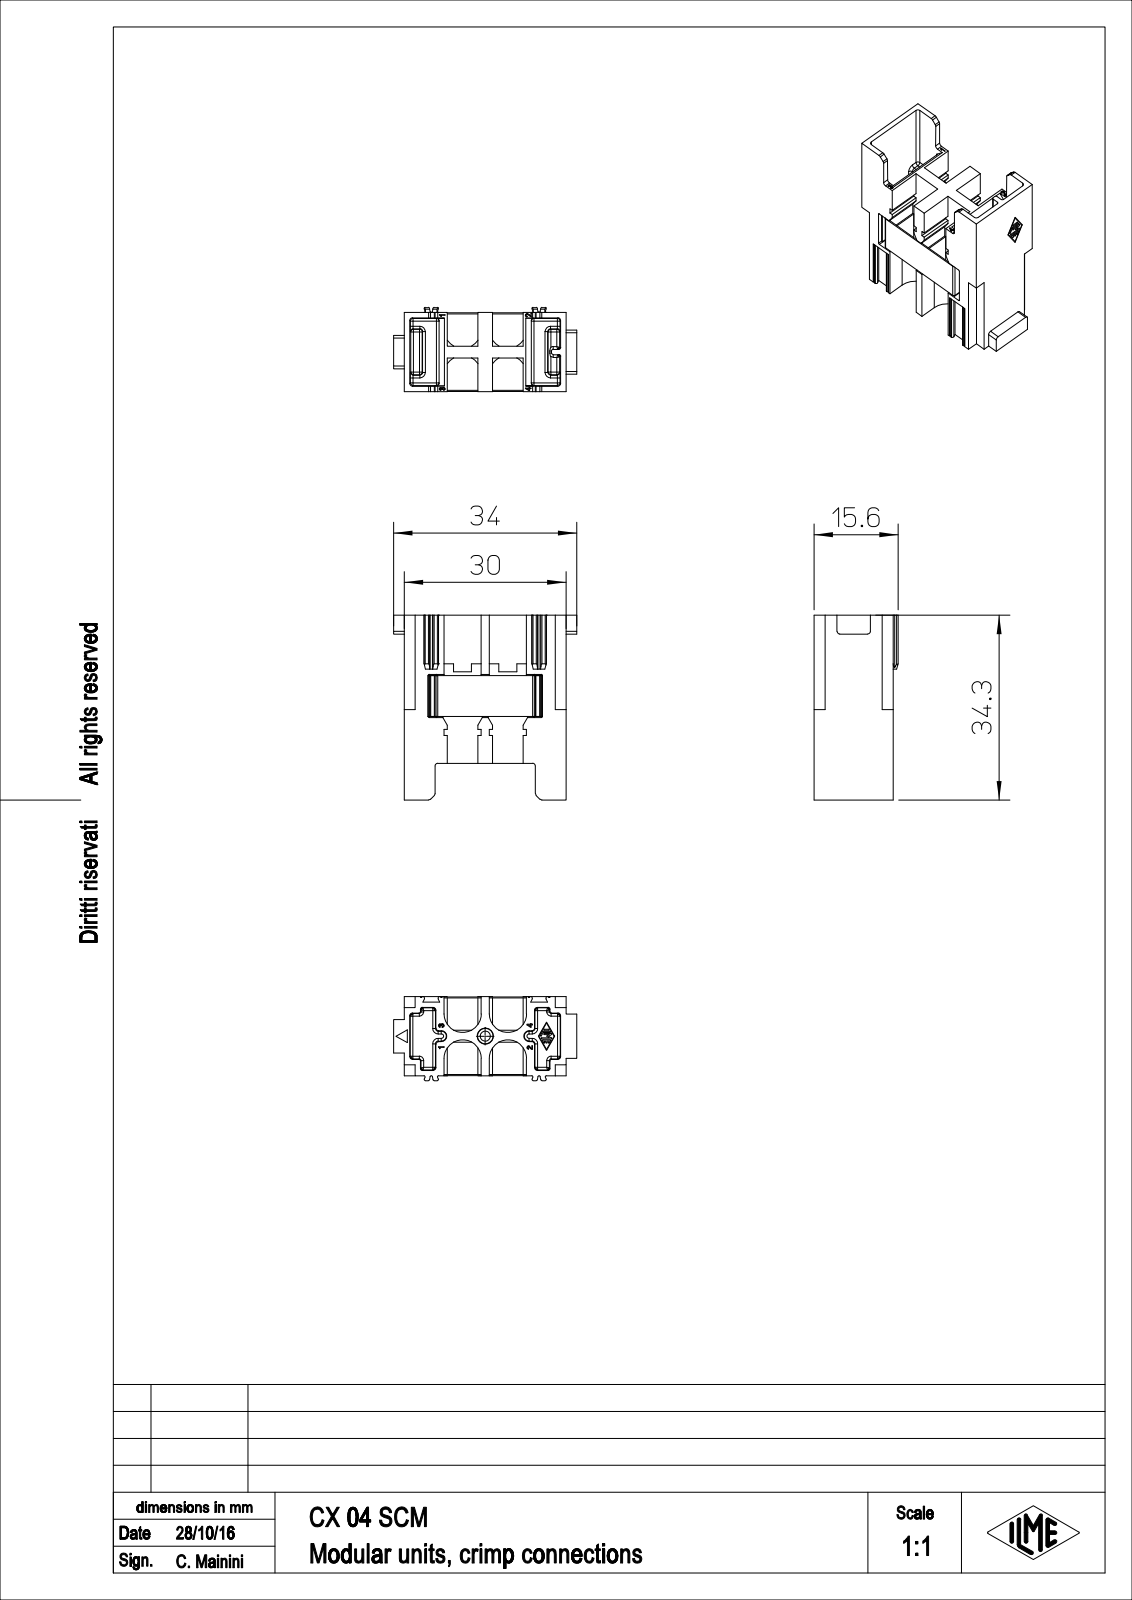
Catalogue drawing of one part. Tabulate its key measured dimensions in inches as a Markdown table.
| quantity | value |
| --- | --- |
| part name | CX_04_SCM |
| STEP written by | PTC Creo Elements/Direct Modeling 19.0E 27-Jun-2016 (C) Parametric Technology GmbH (AUTOMOTIVE_DESIGN) |
| units | inches |
| bodies | 1 solid, 512 faces (408 planar, 88 cylindrical, 16 other) |
| overall size | 1.35 × 1.339 × 0.614 |
| volume | 0.4 in³ |
| surface area | 11.38 in² |
| partial cylindrical surfaces (radius × count) | 0.008 × 34, 0.004 × 16, 0.012 × 16, 0.136 × 4, 0.02 × 2 |
| main face-to-face distances | 0.331, 0.246, 0.333, 0.579, 1.181, 0.059, 0.307, 0.024, 0.248, 0.272 |
